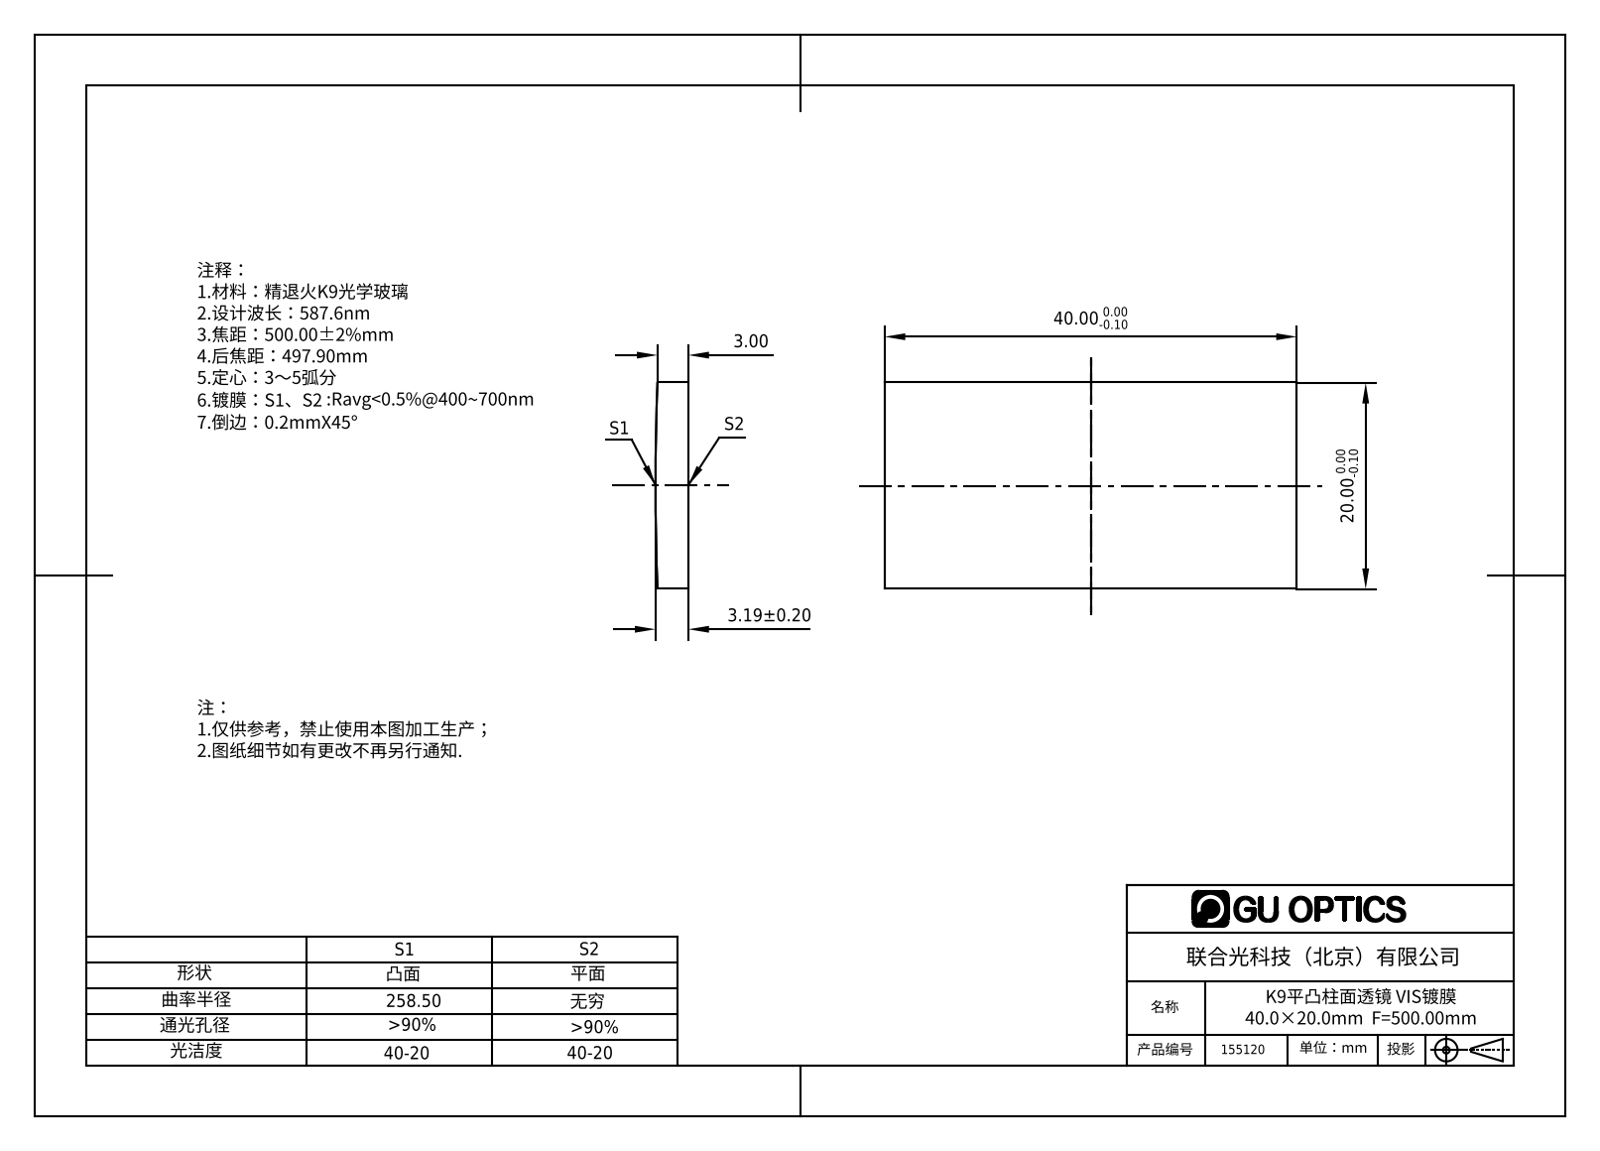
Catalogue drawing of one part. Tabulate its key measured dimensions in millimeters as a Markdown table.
| quantity | value |
| --- | --- |
| part name | 155054 |
| STEP written by | SolidWorks 2016 (AUTOMOTIVE_DESIGN) |
| units | millimeters |
| bodies | 1 solid, 6 faces (5 planar, 1 cylindrical, 0 other) |
| overall size | 40 × 20 × 3.19 |
| volume | 2 500 mm³ |
| surface area | 1 965 mm² |
| partial cylindrical surfaces (radius × count) | 258.5 × 1 |
| main face-to-face distances | 20, 40 |
